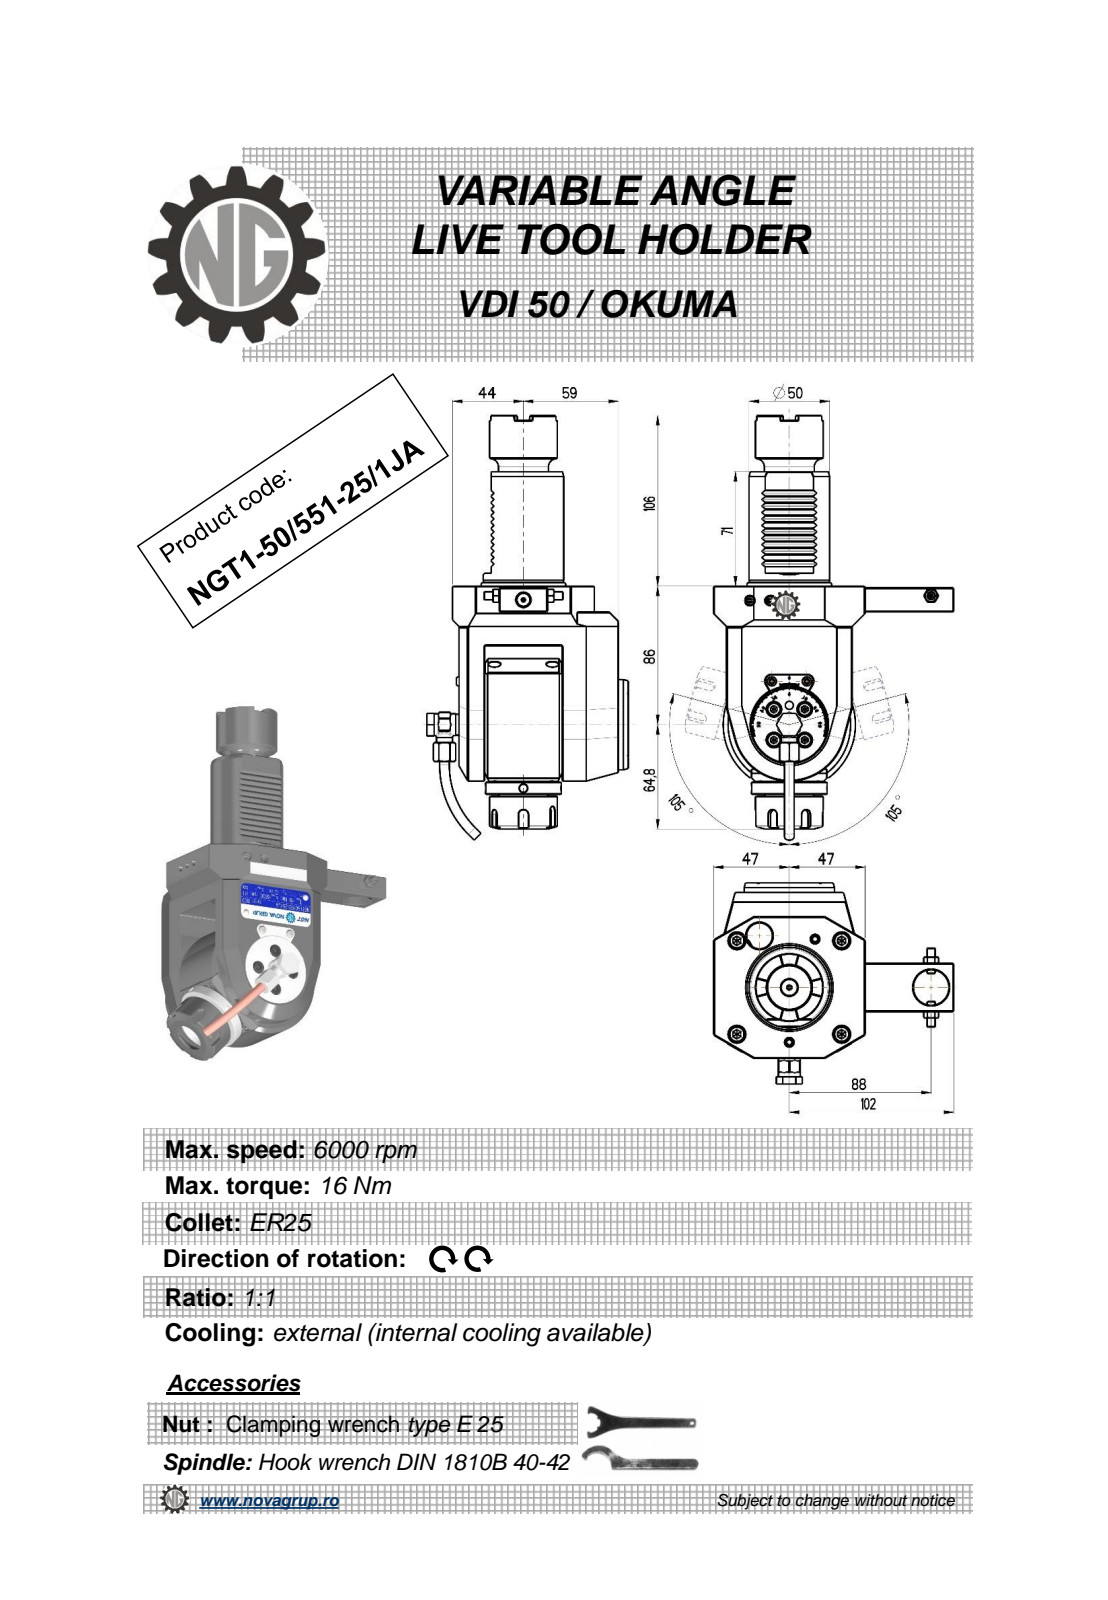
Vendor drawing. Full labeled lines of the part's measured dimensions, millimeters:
Part name (STEP PRODUCT): NGT1_50_551_25_1JA
STEP written by: PRO/ENGINEER BY PARAMETRIC TECHNOLOGY CORPORATION, 2010280 (CONFIG_CONTROL_DESIGN)
Units: millimetres
Bodies: 1 solid, 658 faces (280 planar, 142 cylindrical, 236 other)
Overall size (bounding box): 263.67 × 149 × 124.9
Volume: 1 054 000 mm³ · Surface area: 97 825 mm²
Round holes (diameter × count): ⌀4 ×3, ⌀5 ×2, ⌀3 ×1, ⌀6.2 ×1, ⌀9 ×1, ⌀9.5 ×1, ⌀11 ×1, ⌀20.3 ×1, ⌀22 ×1, ⌀28 ×1
Round bosses / shafts (diameter × count): ⌀10 ×2, ⌀6 ×2, ⌀5.7 ×2, ⌀82 ×1, ⌀56 ×1, ⌀50 ×1, ⌀47 ×1, ⌀42 ×1
Partial cylindrical surfaces — rounded edges, fillets, slot ends (radius × count): R0.26 ×12, R0.3 ×12, R0.16 ×6, R3 ×5, R0.5 ×4, R1 ×2, R10 ×2, R7.7 ×1
Main face-to-face distances: 16, 37, 99, 21, 35, 6, 8, 64, 105, 20
Hole centre spacings: 0.4, 39.45, 49, 49.4, 88, 100.72, 100.92, 116.95
